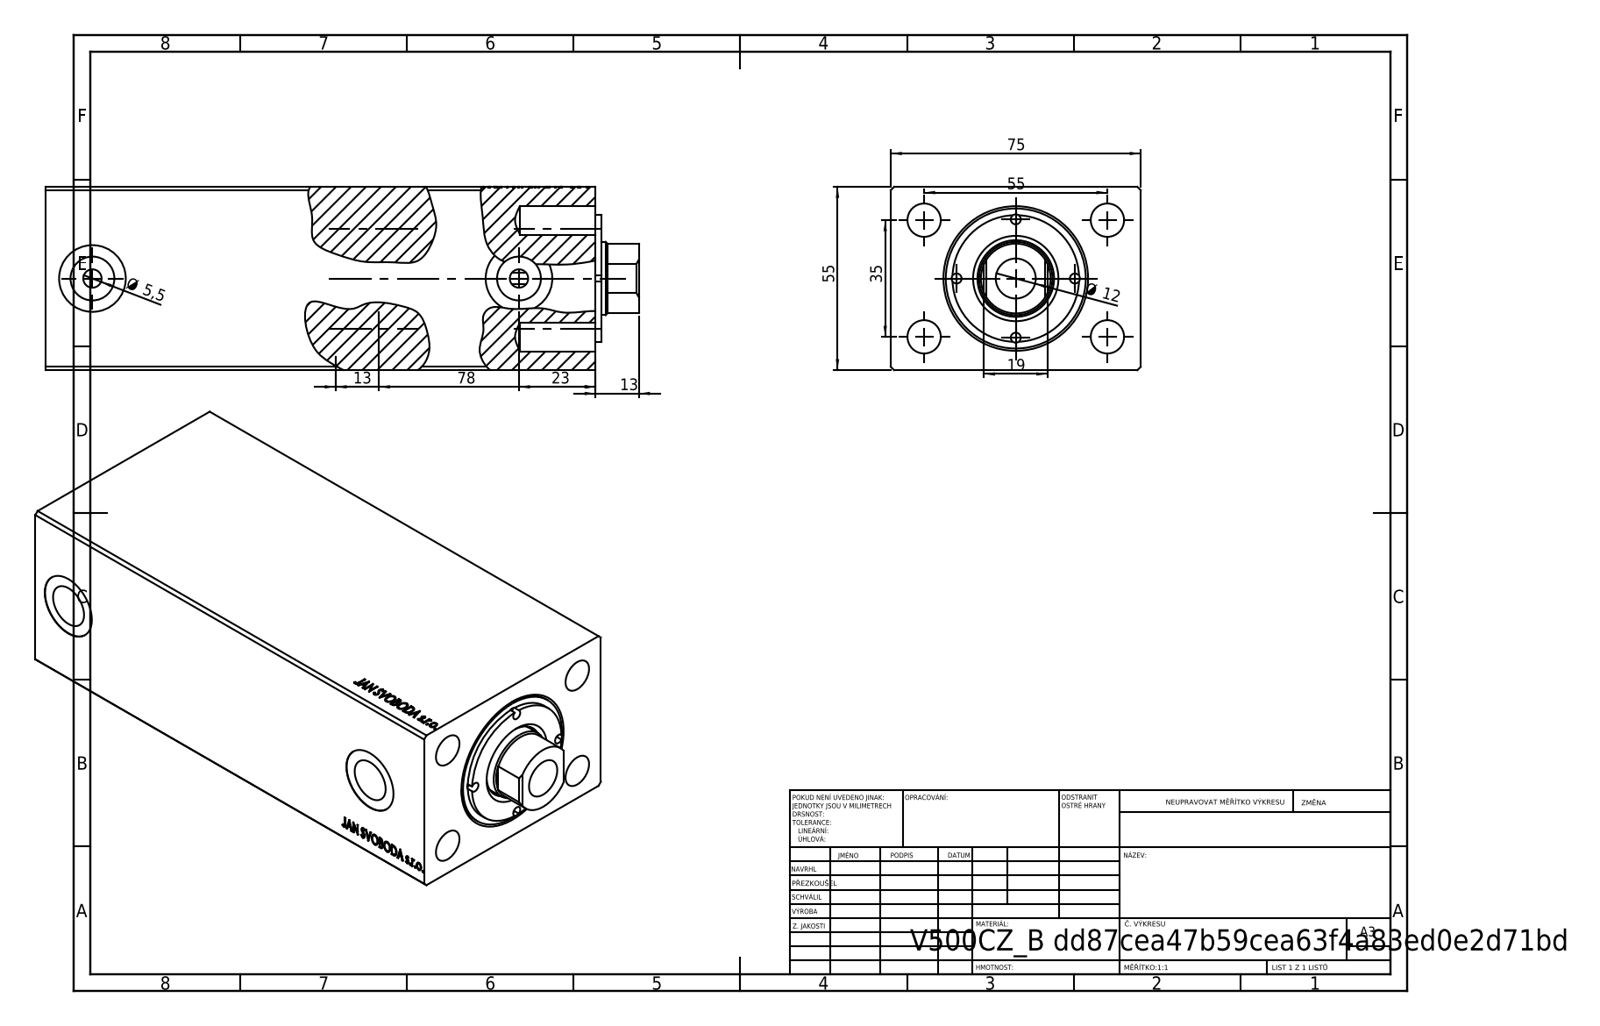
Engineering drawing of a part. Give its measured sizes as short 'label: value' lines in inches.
name: V500CZ_vnitrni_cast_vysunovaci; V500CZ
written by: SolidWorks 2019 (CONFIG_CONTROL_DESIGN)
unit: in
bodies: 3 solids, 873 faces (402 planar, 61 cylindrical, 410 other)
size: 7.008 × 2.953 × 2.165
volume: 37.95 in³; area: 139 in²
holes: 4× ⌀0.118, 4× ⌀0.394, 2× ⌀0.217, 2× ⌀0.518, 2× ⌀0.787, 1× ⌀0.472, 1× ⌀0.866, 1× ⌀0.906, 1× ⌀1.26, 1× ⌀1.417, 1× ⌀1.654
bosses: 1× ⌀1.496
rounds: 1× R0.412
face distances: 2.165, 2.953, 6.496, 5.315, 1.181, 0.394, 4.921, 6.102, 6.488, 6.094
hole spacings: 0.699, 0.789, 0.988, 1.083, 1.283, 1.76, 1.91, 1.378
